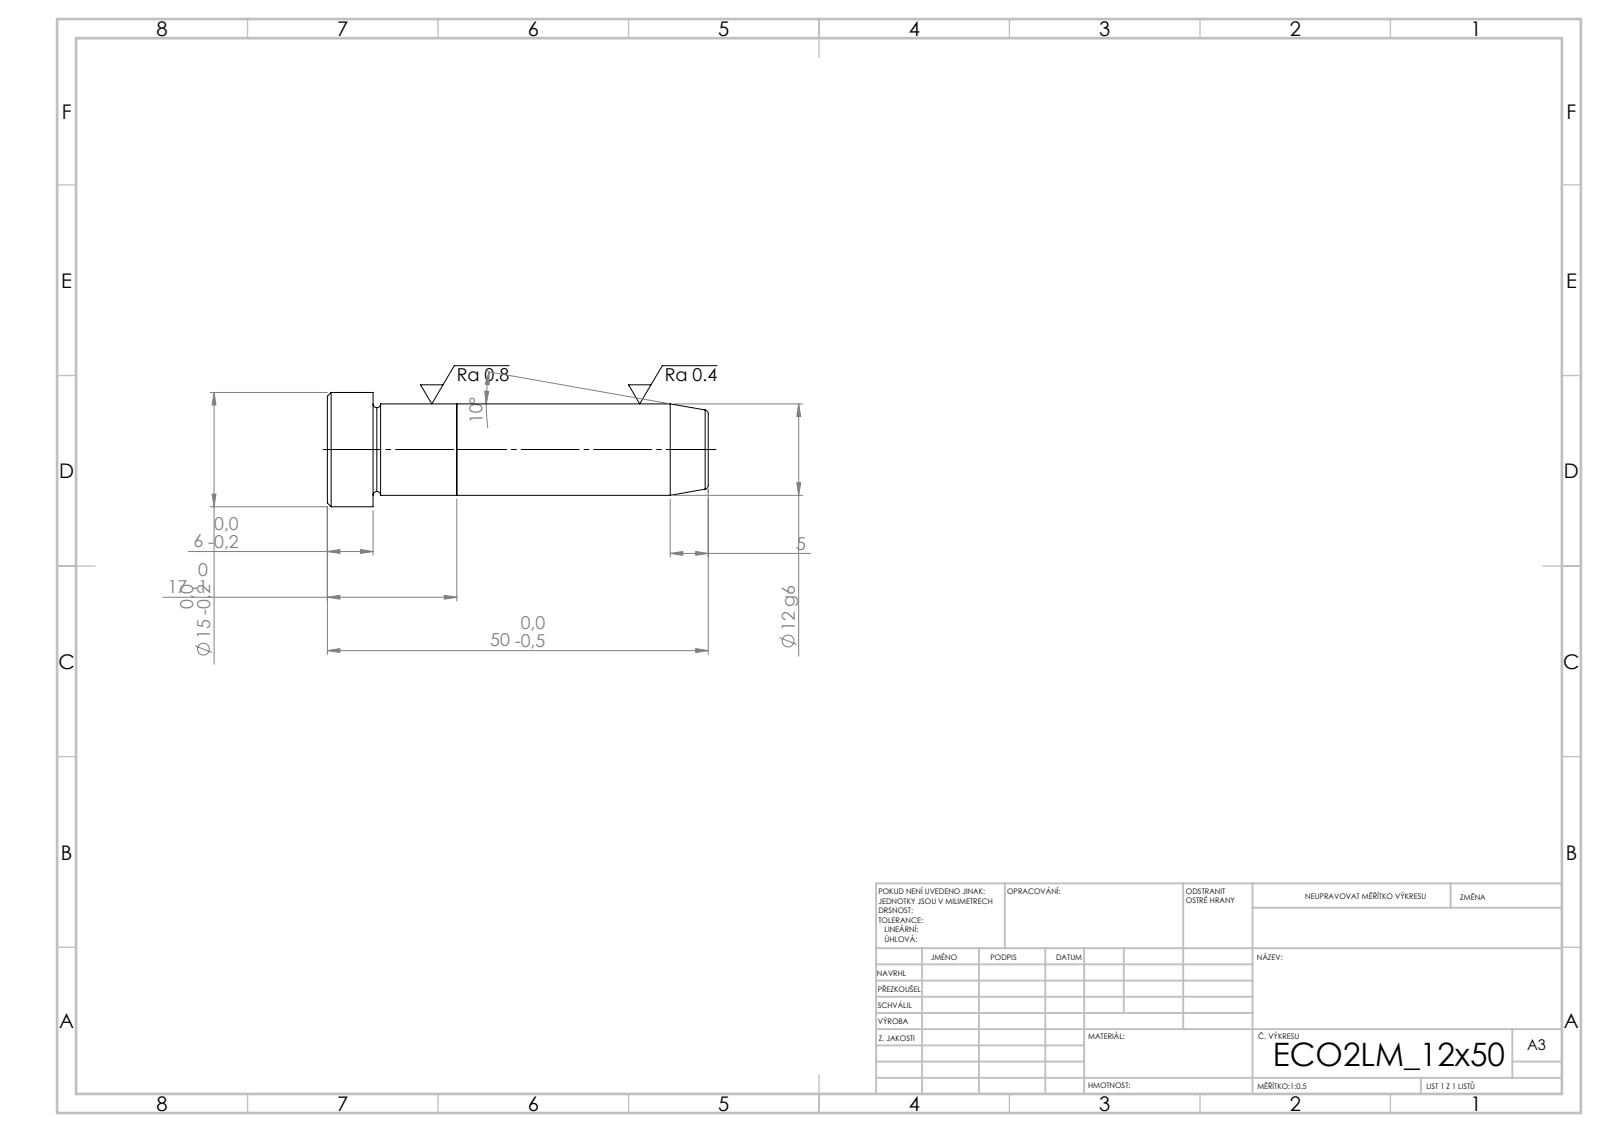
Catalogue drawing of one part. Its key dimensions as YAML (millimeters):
step_written_by: "SolidWorks 2019 (CONFIG_CONTROL_DESIGN)"
units: millimeters
bodies: {solids: 2, faces: 21, planar: 5, cylindrical: 6, other: 10}
overall_size: [50, 15, 15]
volume: 5936
surface_area: 2479
round_bosses_or_shafts:
  - {diameter: 15, count: 1}
  - {diameter: 12, count: 1}
face_to_face_distances: [17, 33, 50, 44, 11, 6]
